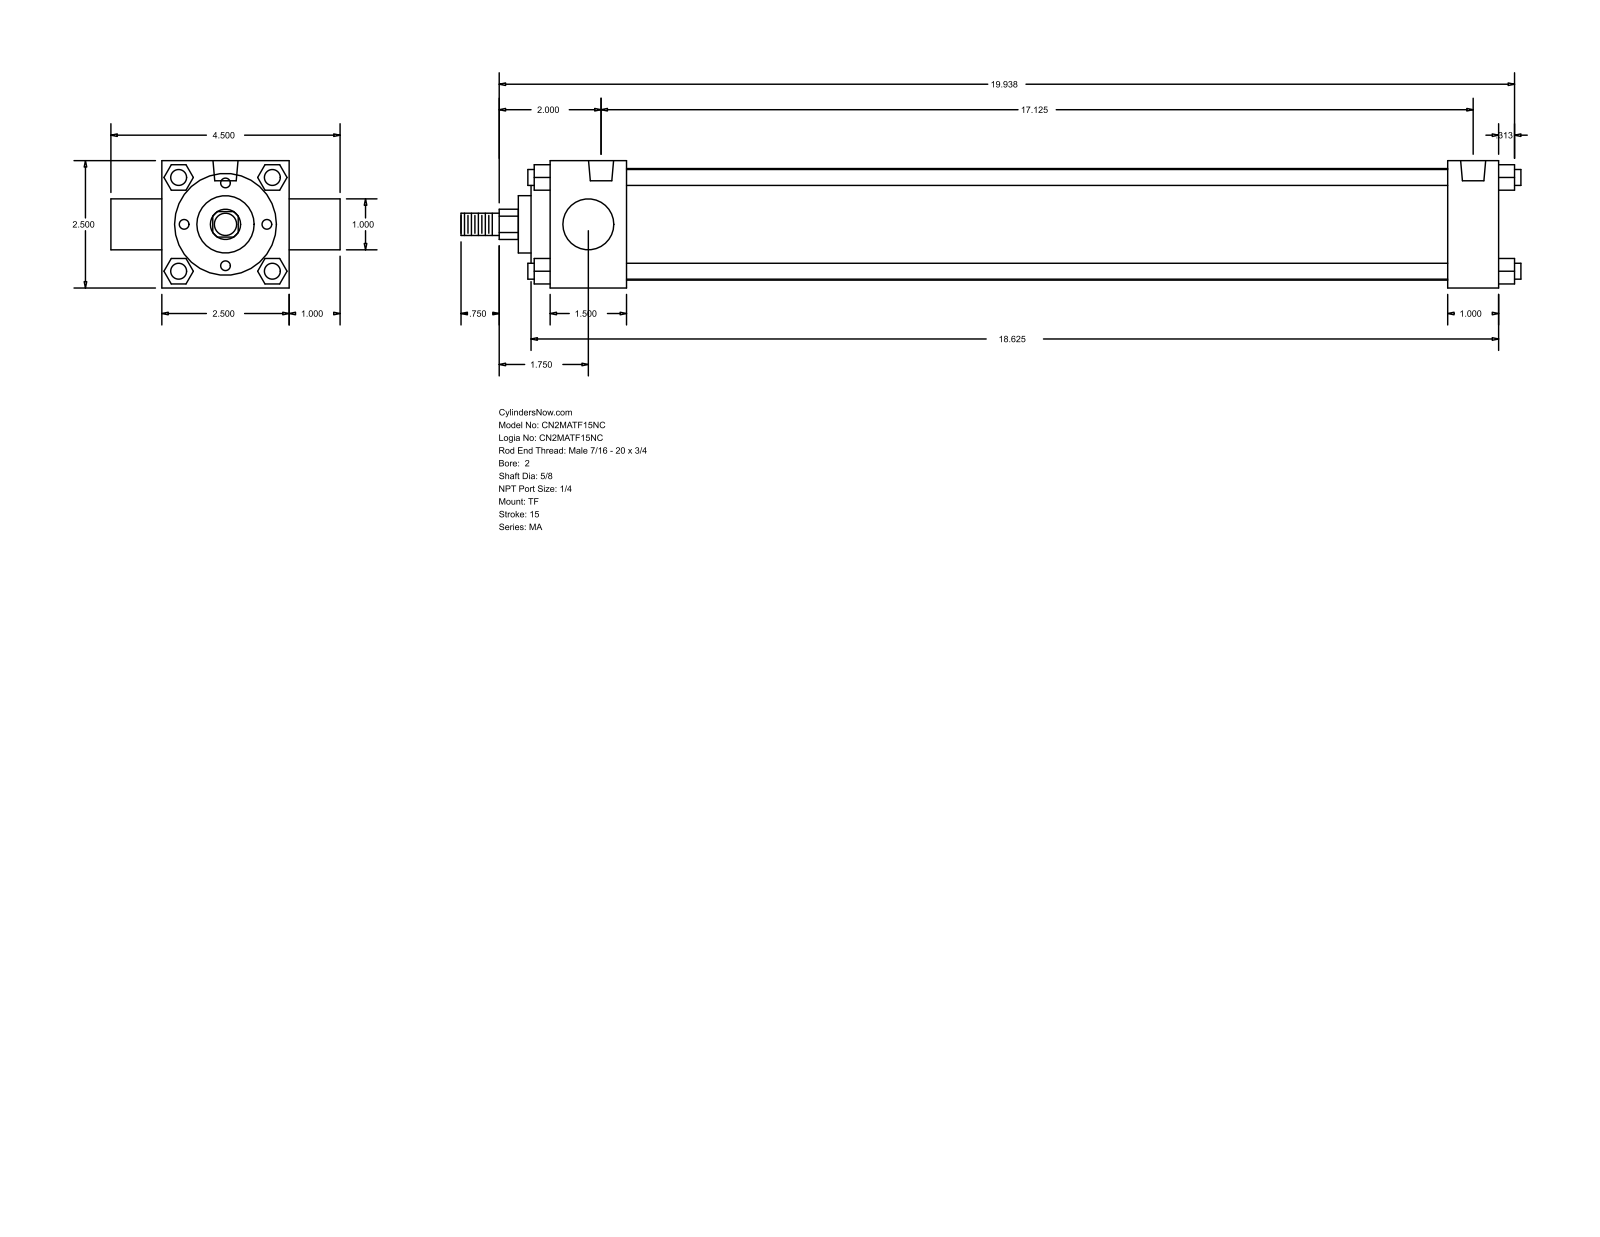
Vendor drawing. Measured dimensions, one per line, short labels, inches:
name: MA_TF__0200_0.625
written by: GSSL Pune (CONFIG_CONTROL_DESIGN)
unit: in
bodies: 0 solids, 122 faces (93 planar, 29 cylindrical, 0 other)
size: 20.813 × 4.5 × 2.5
holes: 3× ⌀0.313, 2× ⌀0.492
bosses: 4× ⌀0.313, 1× ⌀2.19, 1× ⌀2, 1× ⌀1.125, 1× ⌀1, 1× ⌀0.625, 1× ⌀0.437
rounds: 1× R0.297
face distances: 2.5, 1.5, 0.5, 18.625, 17.625, 16.125, 17.125, 1, 0.375, 1.875
hole spacings: 17.125
